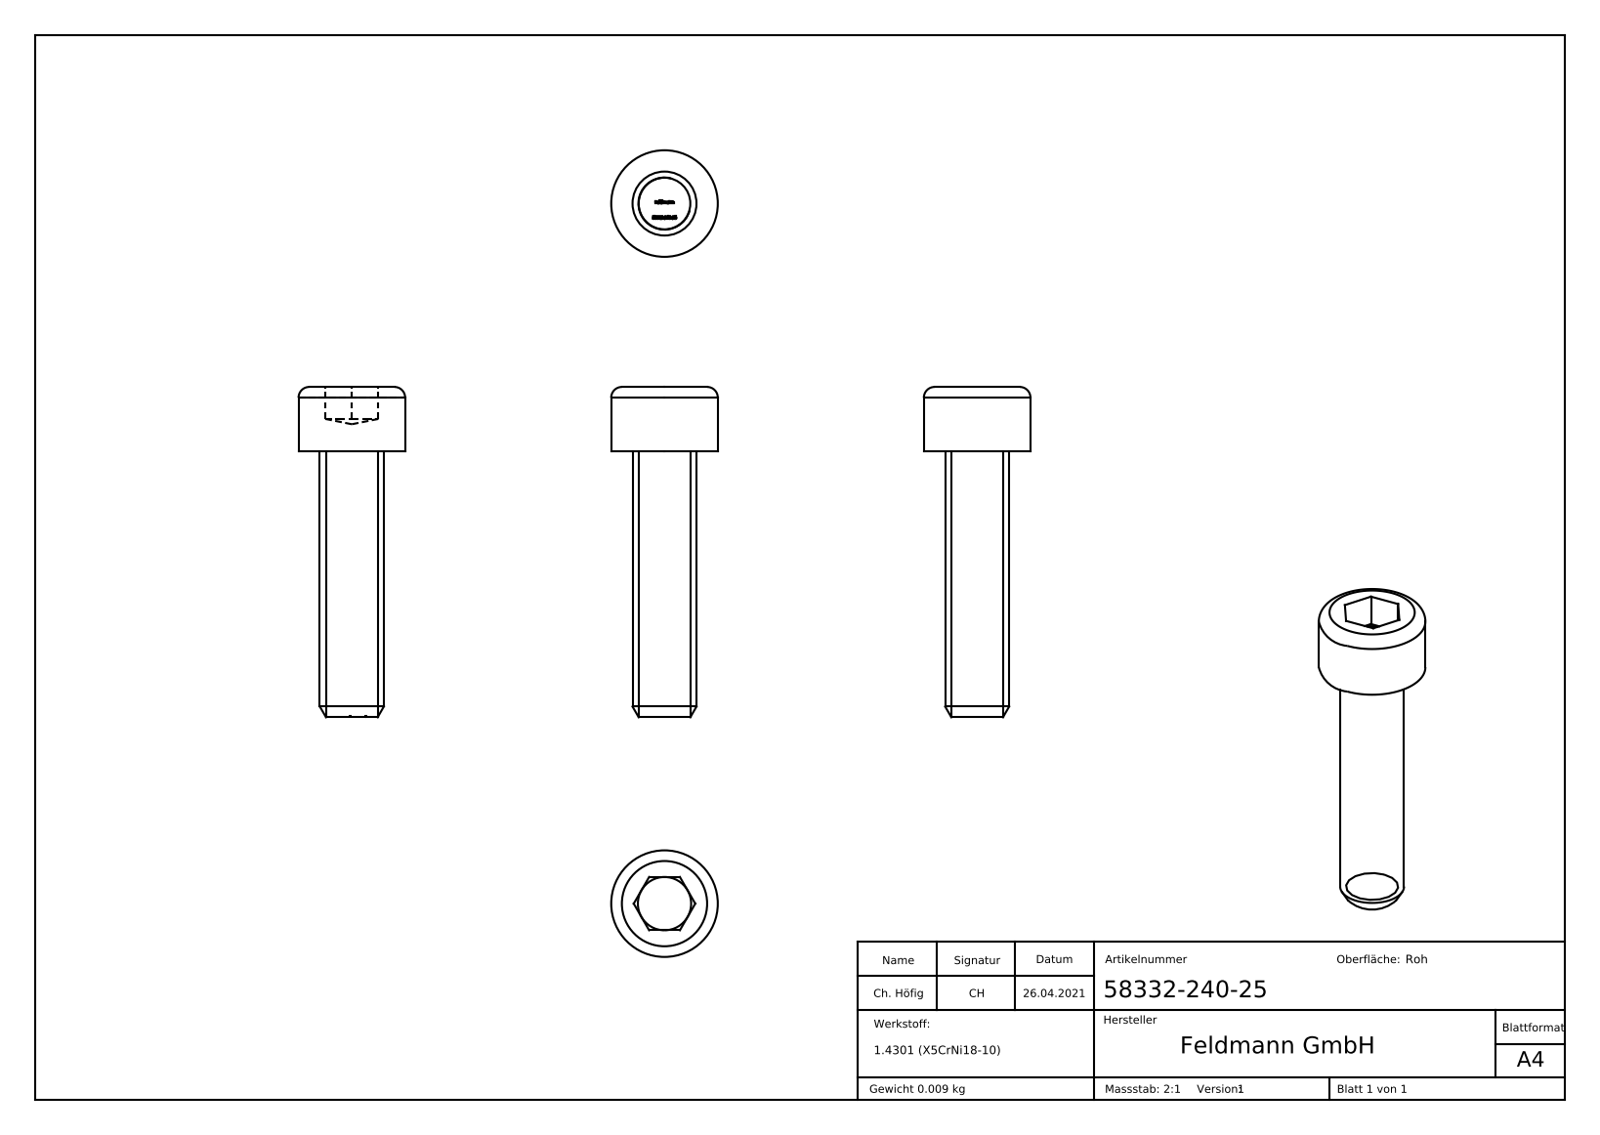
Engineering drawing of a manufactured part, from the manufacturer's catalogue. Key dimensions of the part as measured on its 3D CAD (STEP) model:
Part name (STEP PRODUCT): 58332-240-25
STEP written by: SolidWorks 2018 (CONFIG_CONTROL_DESIGN)
Units: millimetres
Bodies: 1 solid, 299 faces (153 planar, 4 cylindrical, 142 other)
Overall size (bounding box): 91.9 × 10 × 10
Volume: 1 098 mm³ · Surface area: 848 mm²
Round bosses / shafts (diameter × count): ⌀10 ×1, ⌀6 ×1
Main face-to-face distances: 6, 5, 25, 31, 3, 28, 24.9, 27.9, 30.9, 0.54
